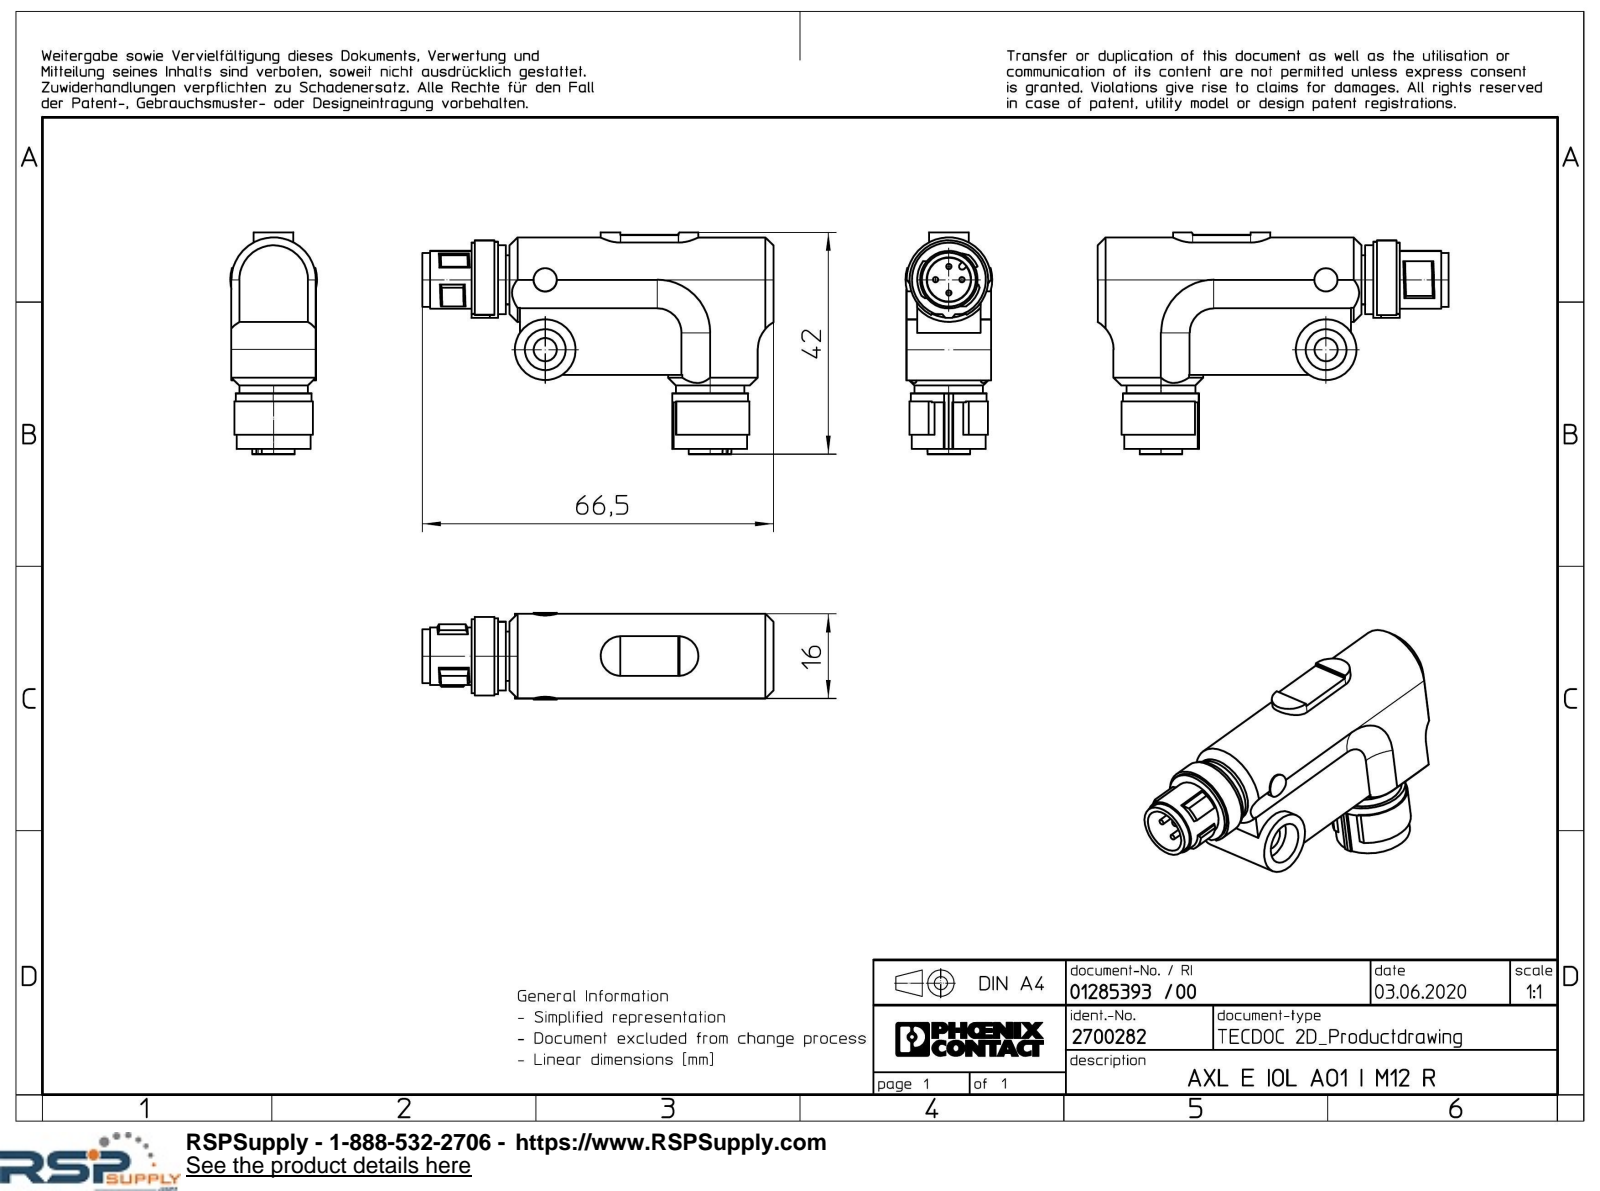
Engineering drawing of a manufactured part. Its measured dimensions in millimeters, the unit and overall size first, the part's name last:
Units: millimetres
Overall size (bounding box): 66.5 × 41.99 × 16.4
Round holes (diameter × count): ⌀1.1 ×4, ⌀1.8 ×1, ⌀4.4 ×1, ⌀7.75 ×1, ⌀11.02 ×1
Round bosses / shafts (diameter × count): ⌀1 ×4, ⌀14.9 ×2, ⌀14.4 ×2, ⌀14 ×2, ⌀13 ×2, ⌀11.5 ×1, ⌀10.9 ×1, ⌀10.2 ×1
Partial cylindrical surfaces — rounded edges, fillets, slot ends (radius × count): R8 ×6, R3.75 ×2, R6 ×2, R0.6 ×1, R0.7 ×1, R8.2 ×1
Main face-to-face distances: 2, 14, 12, 16, 3, 2.7, 26.49, 0.7, 1.5, 12.8
Hole centre spacings: 2.5, 3.54, 5
Volume: 20 333 mm³ · Surface area: 6 914 mm²
Bodies: 1 solid, 171 faces (82 planar, 62 cylindrical, 27 other)
Part name (STEP PRODUCT): AXL_E_IOL_..._..._M12_R-select
STEP written by: Creo Elements/Direct Modeling 20.1A 29-Sep-2018 (C) Parametric Technology GmbH (AUTOMOTIVE_DESIGN)
